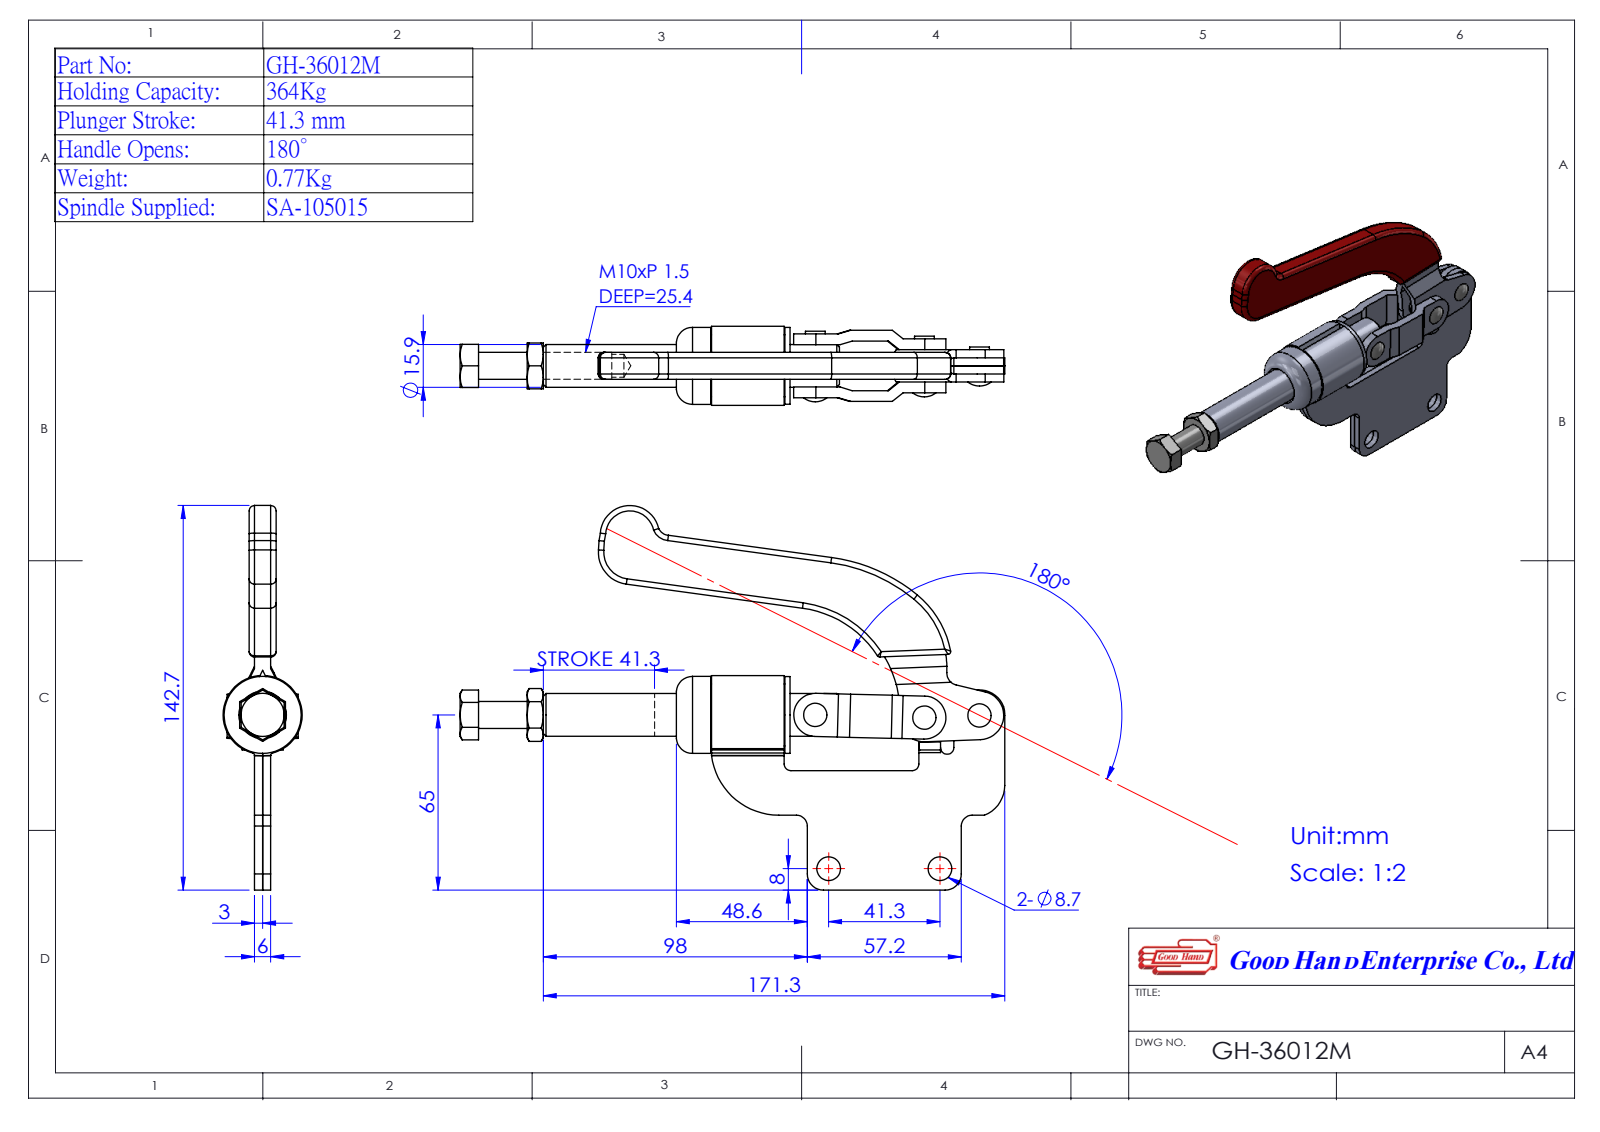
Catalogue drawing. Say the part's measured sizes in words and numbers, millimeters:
The part is named "GH-36012M(簡化)-1; Group1^GH-36012M(簡化); 436010M33-1^GH-36012M(簡化)-1; Group5^GH-36012M(簡化)-1 (+2 more)". Its 3-D file was written by "SolidWorks 2016 (AUTOMOTIVE_DESIGN)". It is 6 solids with 267 faces: 119 planar, 106 cylindrical and 42 other. Overall it measures 202.16 by 142.6 by 29.35 millimeters. Its volume is 99 937 cubic millimeters and its surface area 51 148 square millimeters. Round holes: 2 of diameter 4.5, 2 of diameter 8.8, 1 of diameter 5.74, 1 of diameter 8.5, 1 of diameter 10, 1 of diameter 15.85, 1 of diameter 23.2. Round bosses or shafts: 2 of diameter 5.5, 1 of diameter 28.6, 1 of diameter 28.5, 1 of diameter 23, 1 of diameter 6, 1 of diameter 4.5. Partial cylindrical surfaces (rounded edges, fillets, slot ends): 4 of radius 1, 3 of radius 2.5, 2 of radius 4, 2 of radius 6, 2 of radius 8, 1 of radius 4.27, 1 of radius 4.5, 1 of radius 9. The main face-to-face distances are 6, 3, 2, 8, 5, 10, 11, 1, 9, 4. The hole center spacings are 20.5, 40.5, 41.3, 56.35, 57.36, 58.72, 60.97, 66.36.
